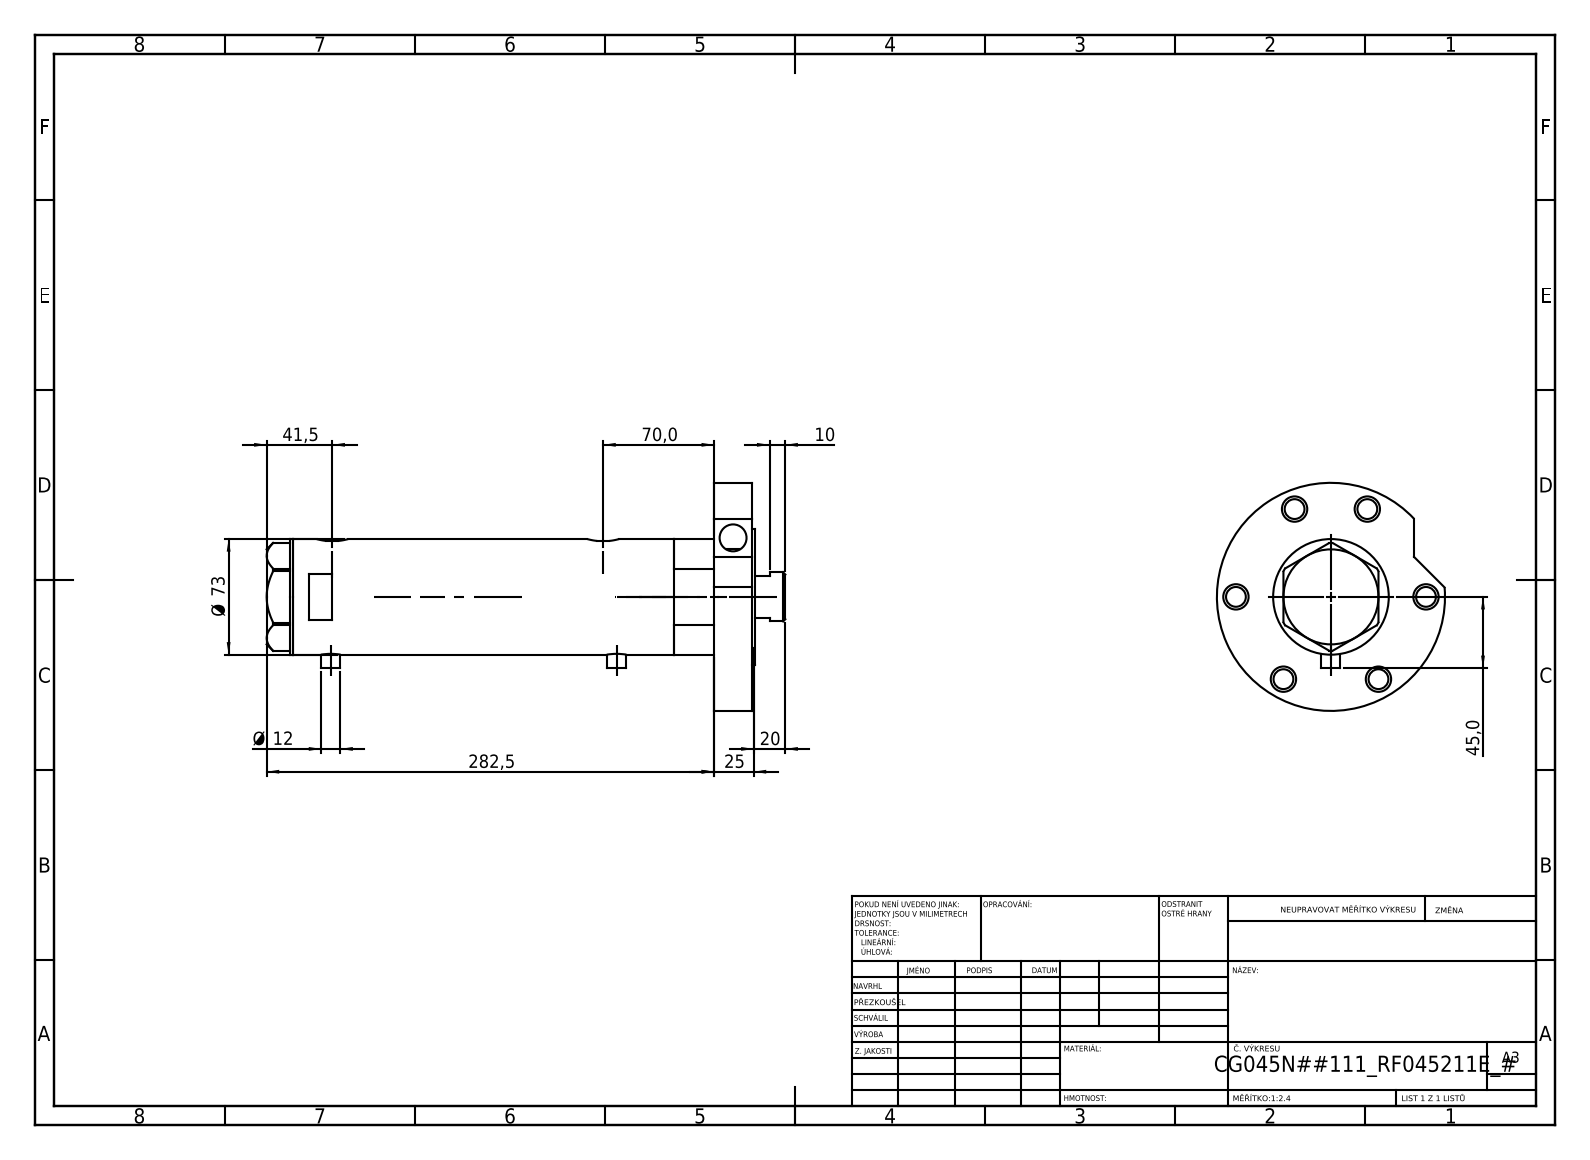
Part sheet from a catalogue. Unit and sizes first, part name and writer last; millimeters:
Units: millimetres
Overall size (bounding box): 327.5 × 144 × 144
Round holes (diameter × count): ⌀12.5 ×8, ⌀16 ×6, ⌀13.16 ×2, ⌀10.5 ×1, ⌀17 ×1, ⌀32 ×1, ⌀33.5 ×1, ⌀45 ×1, ⌀48 ×1, ⌀60 ×1, ⌀64 ×1
Round bosses / shafts (diameter × count): ⌀12 ×2, ⌀144 ×1, ⌀86 ×1, ⌀73 ×1, ⌀58 ×1, ⌀31 ×1
Partial cylindrical surfaces — rounded edges, fillets, slot ends (radius × count): R10 ×2
Main face-to-face distances: 24, 266, 26, 2, 290, 292, 196, 70, 94, 1
Hole centre spacings: 60, 66.67, 99.77, 103.92, 107.62, 119.74, 1, 8.5
Volume: 1 426 000 mm³ · Surface area: 237 376 mm²
Bodies: 5 solids, 164 faces (60 planar, 84 cylindrical, 20 other)
Part name (STEP PRODUCT): V270CG_FRONT; V270CG_VC; V270CG_RF211E; V270CG_MIDDLE (+1 more)
STEP written by: SolidWorks 2019 (CONFIG_CONTROL_DESIGN)
